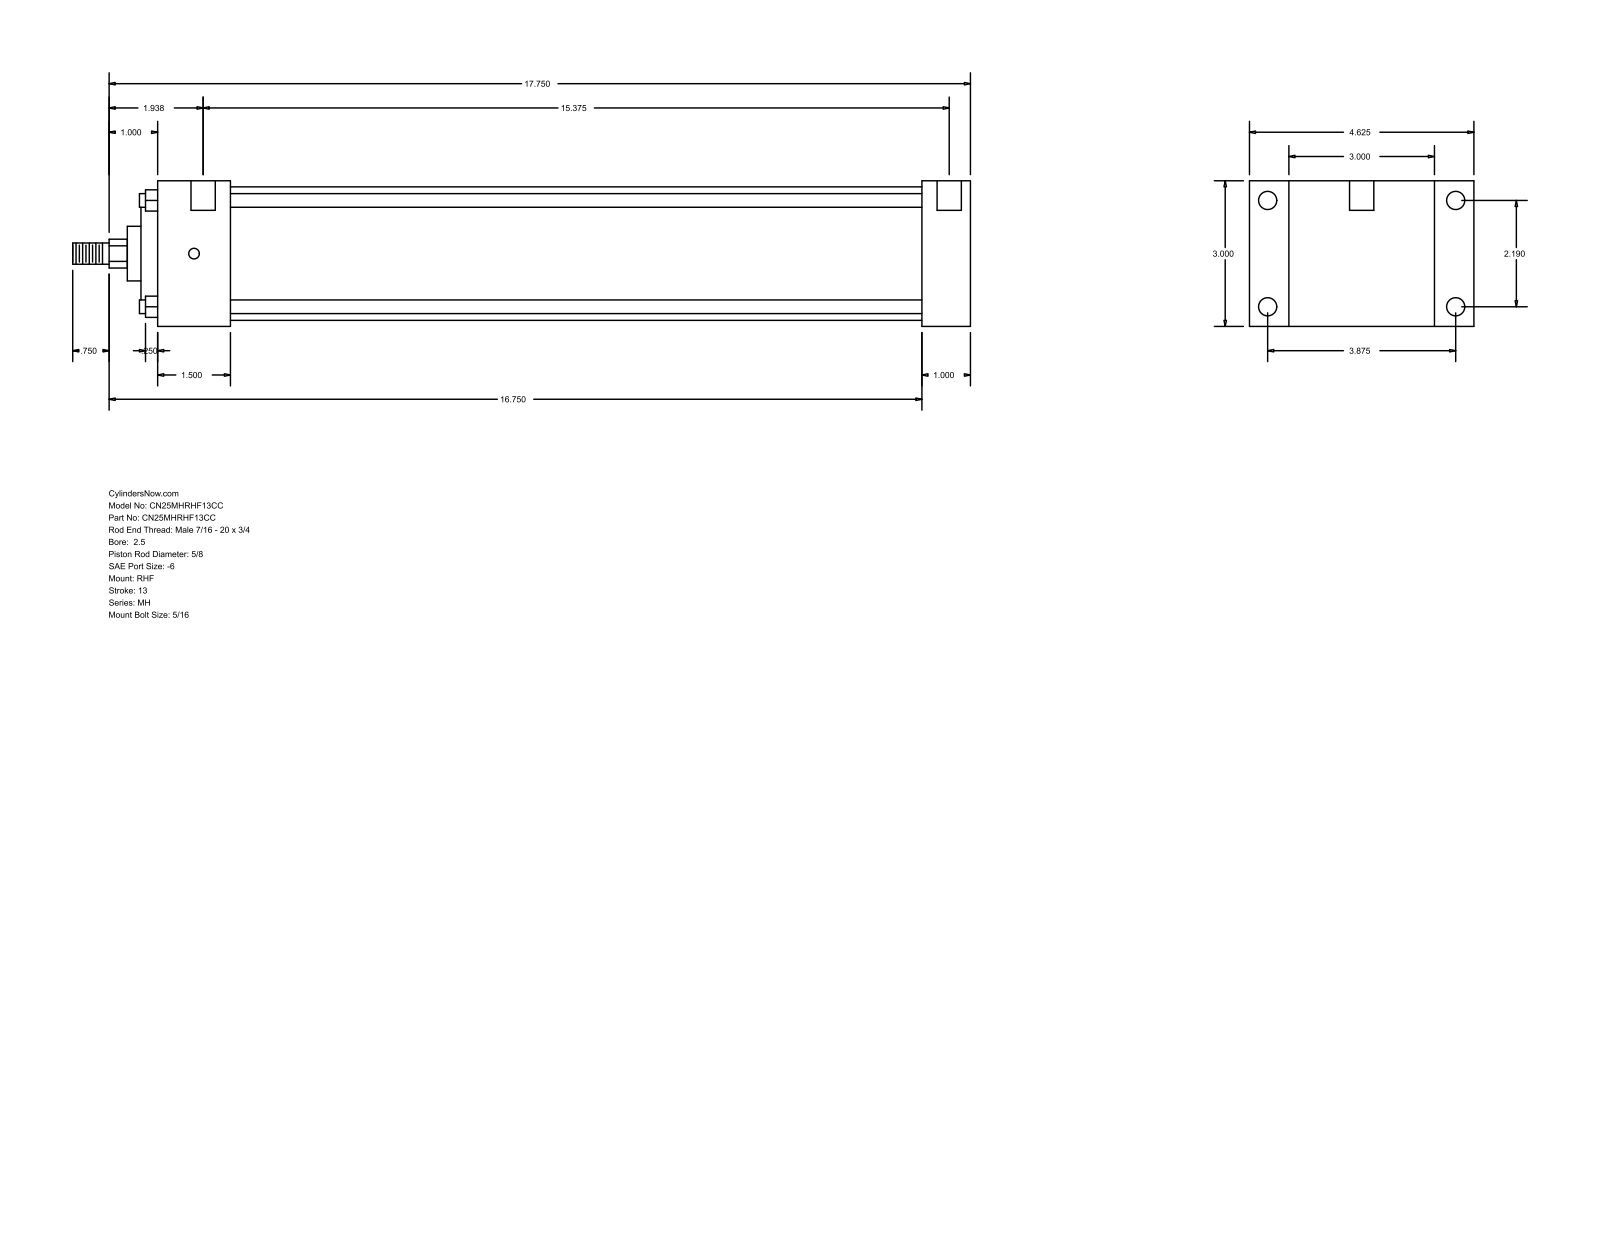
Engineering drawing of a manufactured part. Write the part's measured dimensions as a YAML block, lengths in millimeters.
part_name: "MH_RHF__0250_0.625"
step_written_by: "GSSL Pune (CONFIG_CONTROL_DESIGN)"
units: millimeters
bodies: {solids: 0, faces: 90, planar: 61, cylindrical: 29, other: 0}
overall_size: [469.9, 117.47, 76.2]
round_holes:
  - {diameter: 5.56, count: 4}
  - {diameter: 9.53, count: 4}
  - {diameter: 12.7, count: 2}
round_bosses_or_shafts:
  - {diameter: 7.14, count: 4}
  - {diameter: 69.85, count: 1}
  - {diameter: 55.55, count: 1}
  - {diameter: 28.57, count: 1}
  - {diameter: 15.88, count: 1}
  - {diameter: 11.11, count: 1}
partial_cylinders:
  - {radius: 7.54, count: 1}
face_to_face_distances: [76.2, 25.4, 20.64, 96.84, 425.45, 400.05, 38.1, 117.48, 361.95, 387.35]
hole_center_spacings: [55.62, 98.42, 113.05, 398.46, 3.17, 4.76, 390.53, 393.7]
